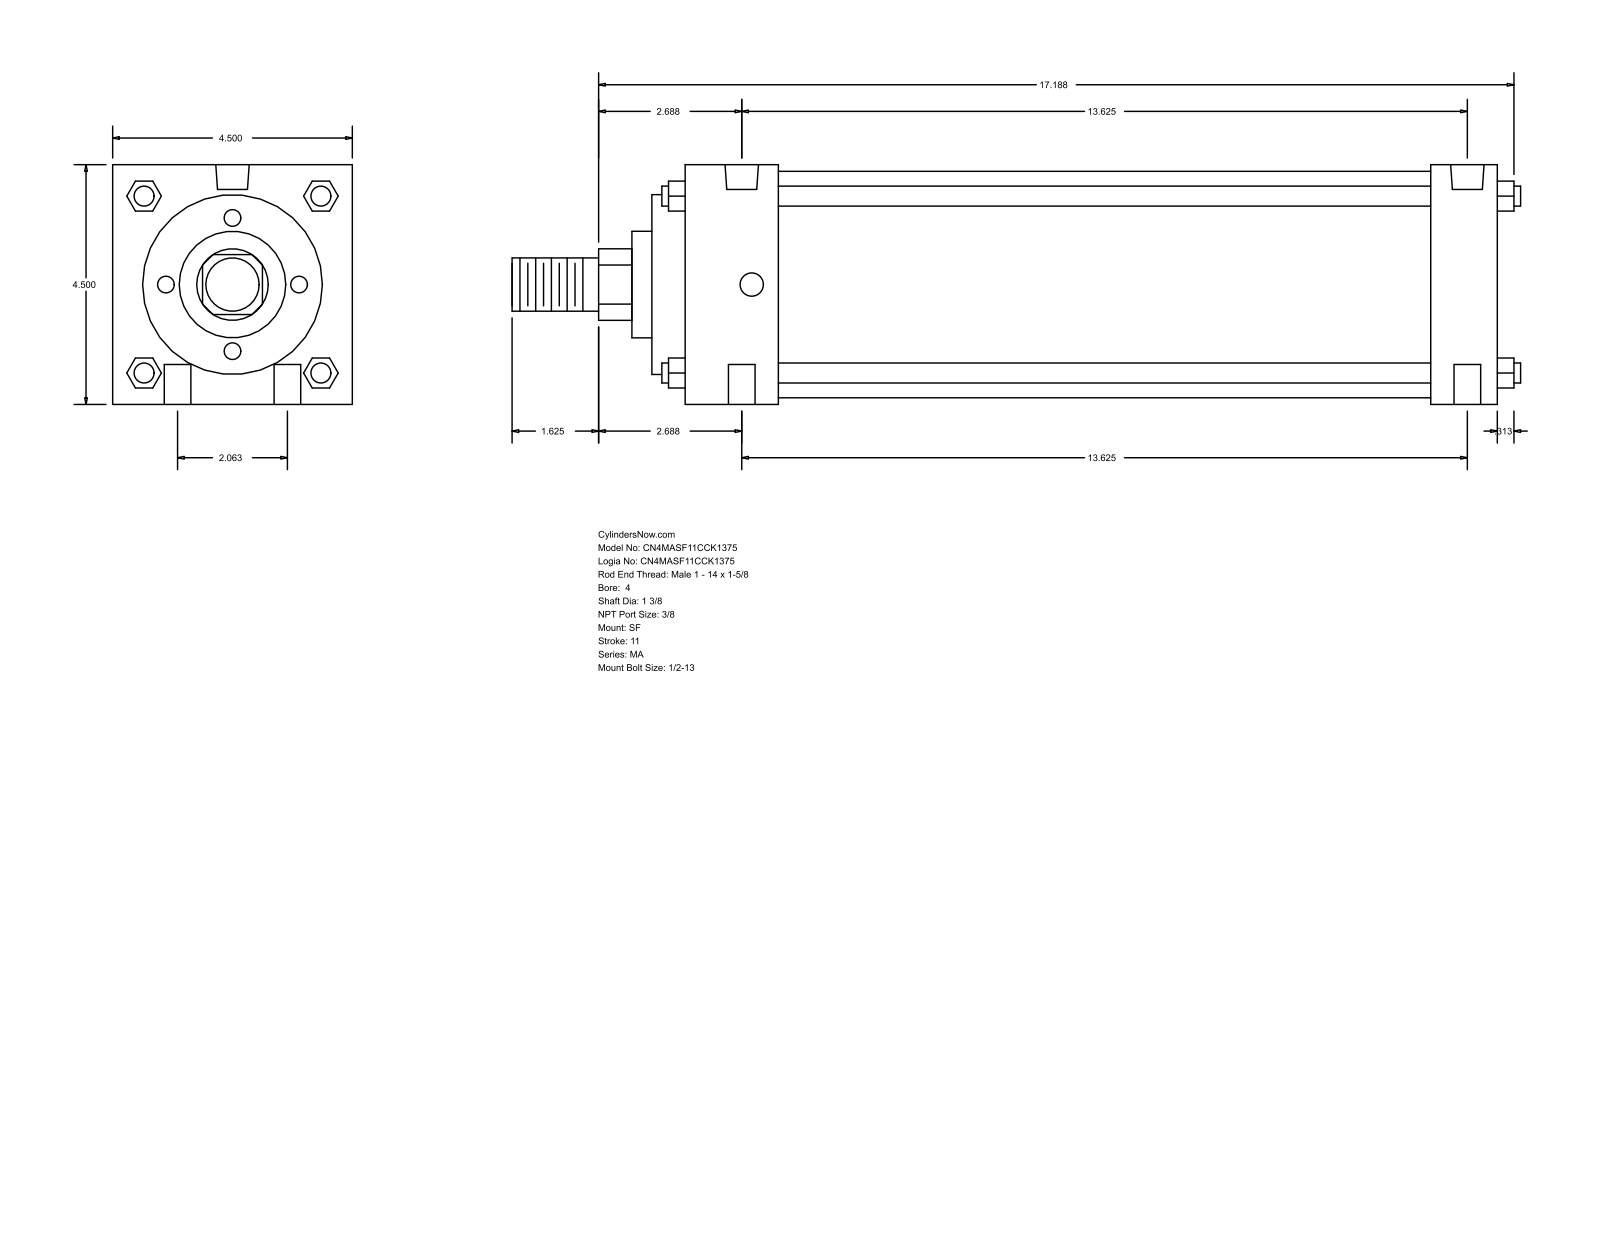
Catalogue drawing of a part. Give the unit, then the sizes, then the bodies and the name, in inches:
Units: inches
Overall size (bounding box): 18.937 × 4.5 × 4.5
Round holes (diameter × count): ⌀0.5 ×4, ⌀0.437 ×2, ⌀0.627 ×2
Round bosses / shafts (diameter × count): ⌀0.375 ×4, ⌀4.25 ×1, ⌀3.375 ×1, ⌀2 ×1, ⌀1.375 ×1, ⌀1 ×1
Partial cylindrical surfaces — rounded edges, fillets, slot ends (radius × count): R0.672 ×1
Main face-to-face distances: 4.5, 15.25, 15.875, 0.625, 14.625, 14, 1.25, 2.375, 1.75, 12.25
Hole centre spacings: 1.031, 13.664, 13.625, 2.062, 13.78, 13.25
Bodies: 0 solids, 126 faces (95 planar, 31 cylindrical, 0 other)
Part name (STEP PRODUCT): MA_SF__0400_1.375
STEP written by: GSSL Pune (CONFIG_CONTROL_DESIGN)
